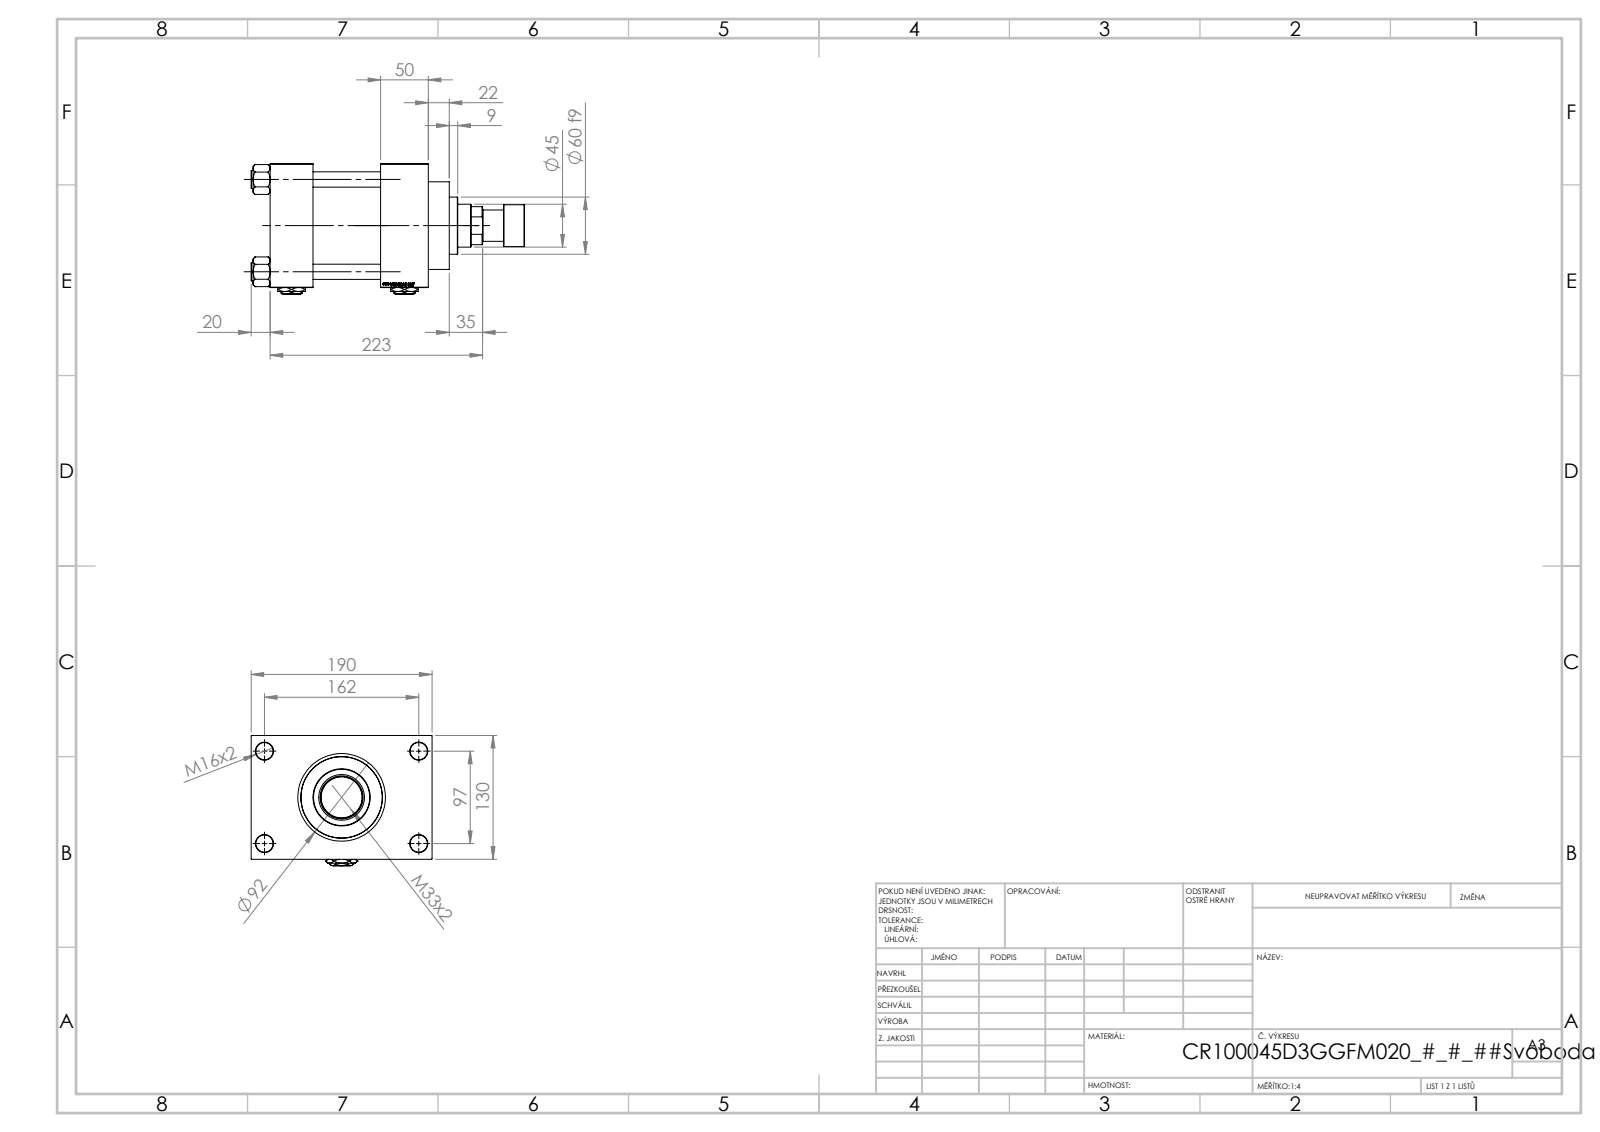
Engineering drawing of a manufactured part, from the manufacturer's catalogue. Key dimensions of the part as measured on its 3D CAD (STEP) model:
Part name (STEP PRODUCT): V215_VC_A; V215CR_ROD_END_F; V215CR_D_Body; V215CR_D_TYCINKA (+3 more)
STEP written by: SolidWorks 2019 (CONFIG_CONTROL_DESIGN)
Units: millimetres
Bodies: 14 solids, 1266 faces (596 planar, 104 cylindrical, 566 other)
Overall size (bounding box): 287 × 190 × 137
Volume: 2 645 000 mm³ · Surface area: 367 691 mm²
Round holes (diameter × count): ⌀16 ×4, ⌀18 ×4, ⌀7 ×2, ⌀26.44 ×2, ⌀35 ×2, ⌀31.5 ×1, ⌀45 ×1, ⌀48 ×1, ⌀76 ×1, ⌀85.5 ×1, ⌀100 ×1
Round bosses / shafts (diameter × count): ⌀19 ×4, ⌀106 ×1, ⌀92 ×1, ⌀60 ×1, ⌀44 ×1, ⌀33 ×1
Main face-to-face distances: 130, 116, 45, 71, 166, 121, 50, 160, 30, 70
Hole centre spacings: 32.55, 68.52, 94.41, 96.9, 102.27, 129.45, 161.73, 97
